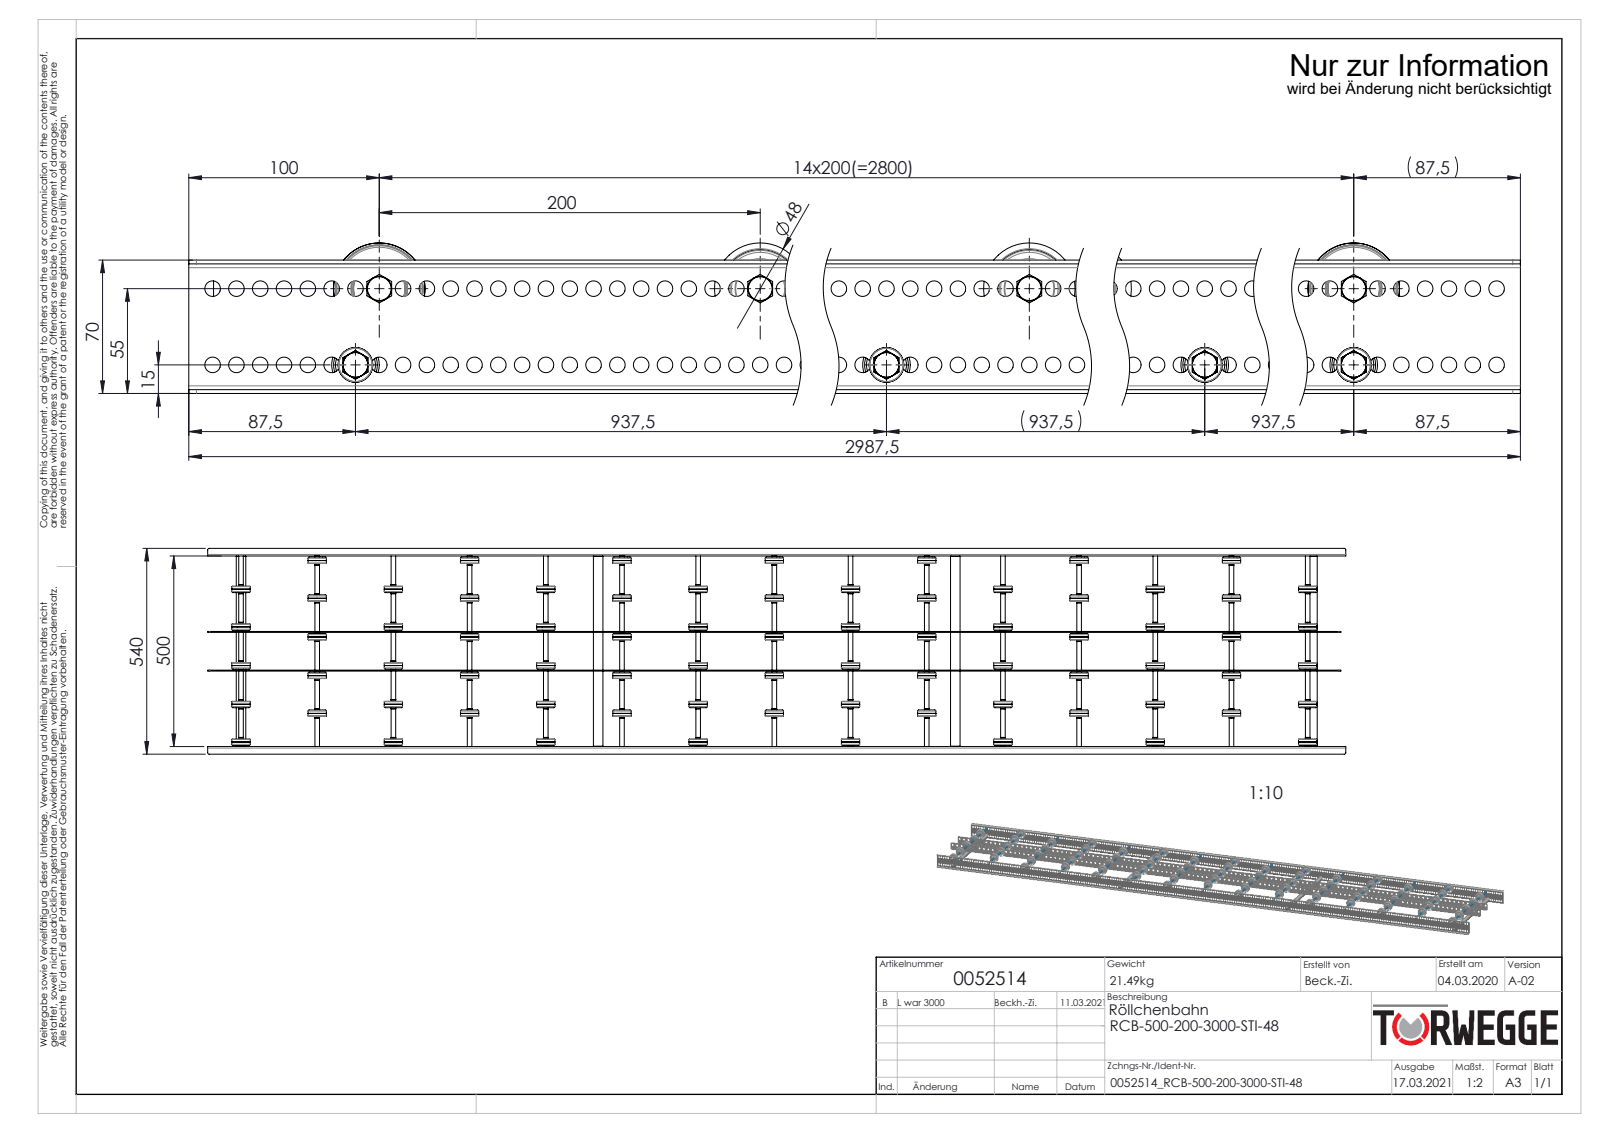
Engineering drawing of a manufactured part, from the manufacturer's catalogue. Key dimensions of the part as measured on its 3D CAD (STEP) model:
Part name (STEP PRODUCT): S100100_Längstraverse-42x2,5_S100104_Lngstraverse-RB-L3000; 0052514; 0046278_KB-ROHR-12X1,75mm_KFG_L75; Röllchenachse-für-Konfiguration_EL500 Stahl (+6 more)
STEP written by: SolidWorks 2020 (AUTOMOTIVE_DESIGN)
Units: millimetres
Bodies: 294 solids, 10318 faces (1836 planar, 4884 cylindrical, 3598 other)
Overall size (bounding box): 2987.5 × 540 × 79
Volume: 4 289 000 mm³ · Surface area: 3 573 000 mm²
Round holes (diameter × count): ⌀8.2 ×476, ⌀8.5 ×119, ⌀6.65 ×15, ⌀8 ×15, ⌀9.65 ×15, ⌀15 ×15, ⌀41 ×15, ⌀6.8 ×4, ⌀21 ×4
Round bosses / shafts (diameter × count): ⌀48 ×15, ⌀13 ×15, ⌀12.5 ×15, ⌀12.4 ×15, ⌀12 ×15, ⌀11.5 ×15, ⌀25 ×4, ⌀8 ×4
Partial cylindrical surfaces — rounded edges, fillets, slot ends (radius × count): R4 ×8, R2 ×4, R5 ×4
Main face-to-face distances: 2, 200.5, 302, 101.5, 502, 200, 202.5, 301.5, 304, 198
Hole centre spacings: 12.5, 25, 37.5, 50, 62.5, 75, 87.5, 100
